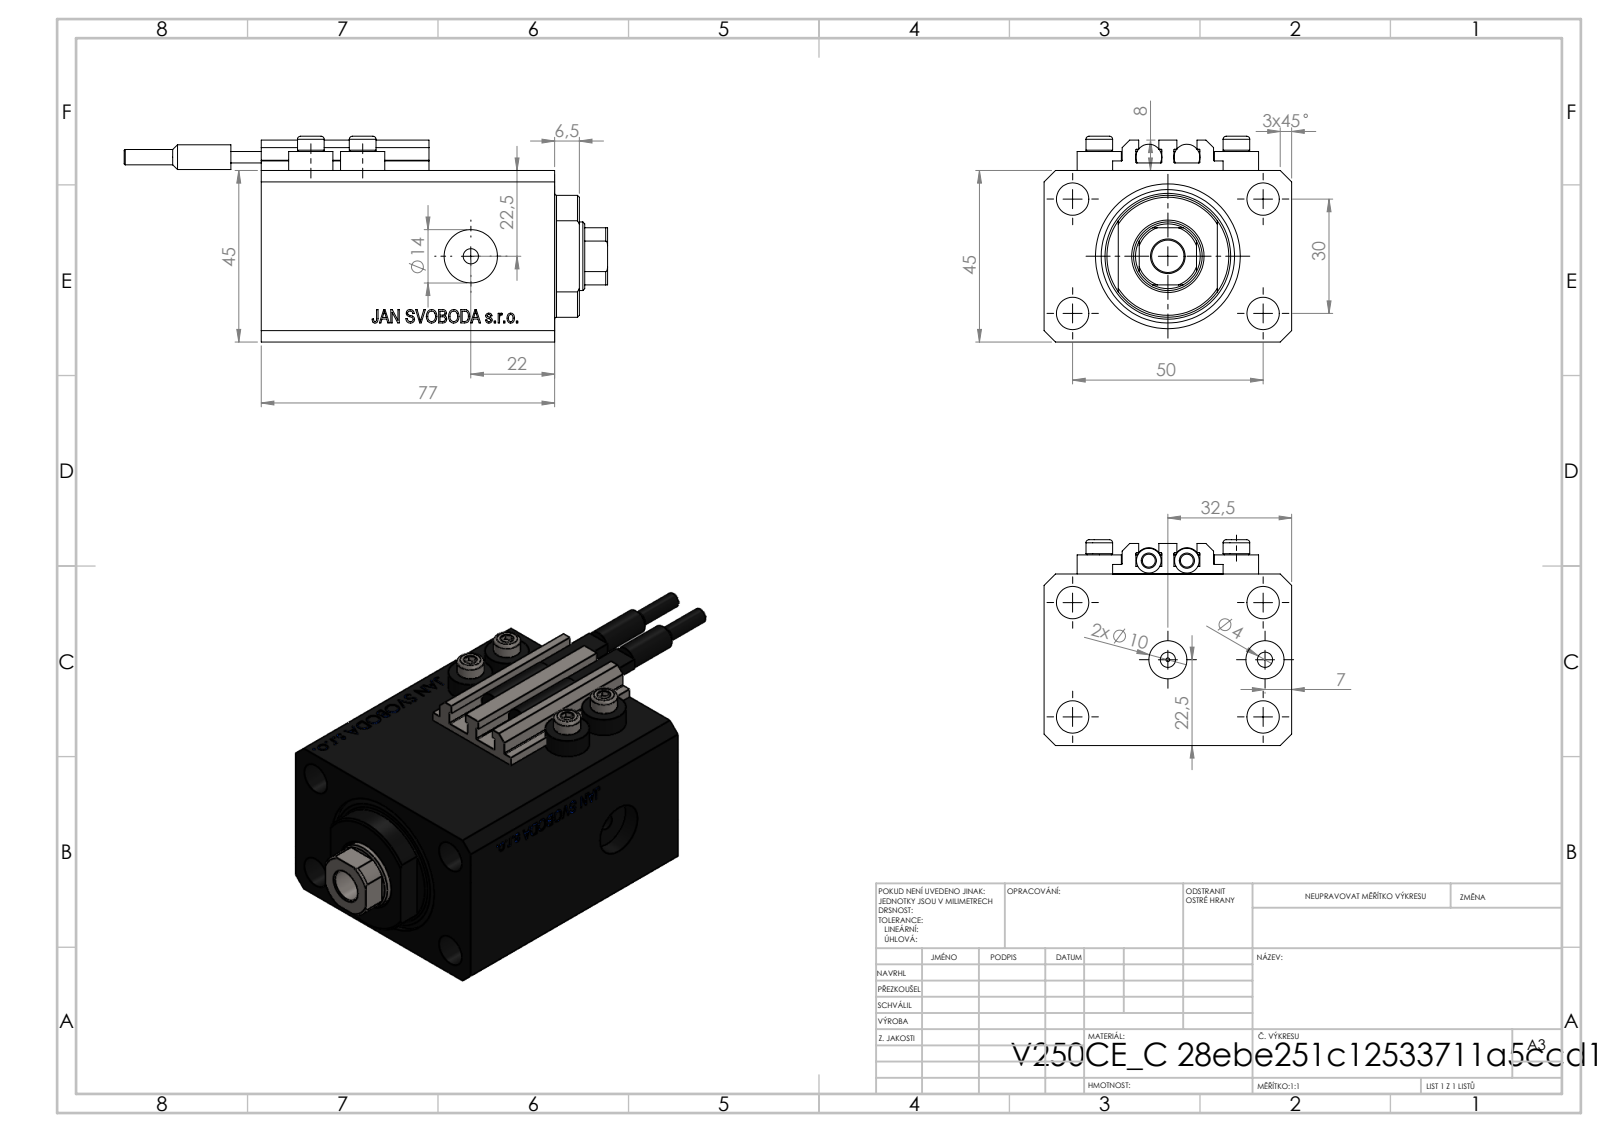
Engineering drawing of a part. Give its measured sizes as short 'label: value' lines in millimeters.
name: SWITCH_V250CE; V250CE_C_Body; ALLEN BOLT V250CE; V250CE_VC_C (+1 more)
written by: SolidWorks 2019 (CONFIG_CONTROL_DESIGN)
unit: mm
bodies: 10 solids, 1094 faces (536 planar, 104 cylindrical, 454 other)
size: 127 × 65 × 54
volume: 215 074 mm³; area: 60 430 mm²
holes: 8× ⌀4, 5× ⌀8.5, 2× ⌀10, 2× ⌀14, 1× ⌀1.25, 1× ⌀18, 1× ⌀25, 1× ⌀38
bosses: 4× ⌀11.6, 4× ⌀7, 2× ⌀6.8, 2× ⌀6.5, 2× ⌀4
rounds: 10× R0.2, 1× R8.5, 1× R16
face distances: 45, 65, 14, 77, 63, 3, 47, 6.9, 56.1, 70.1
hole spacings: 29.15, 13.6, 15.01, 30, 36, 38.48, 50, 52.68
